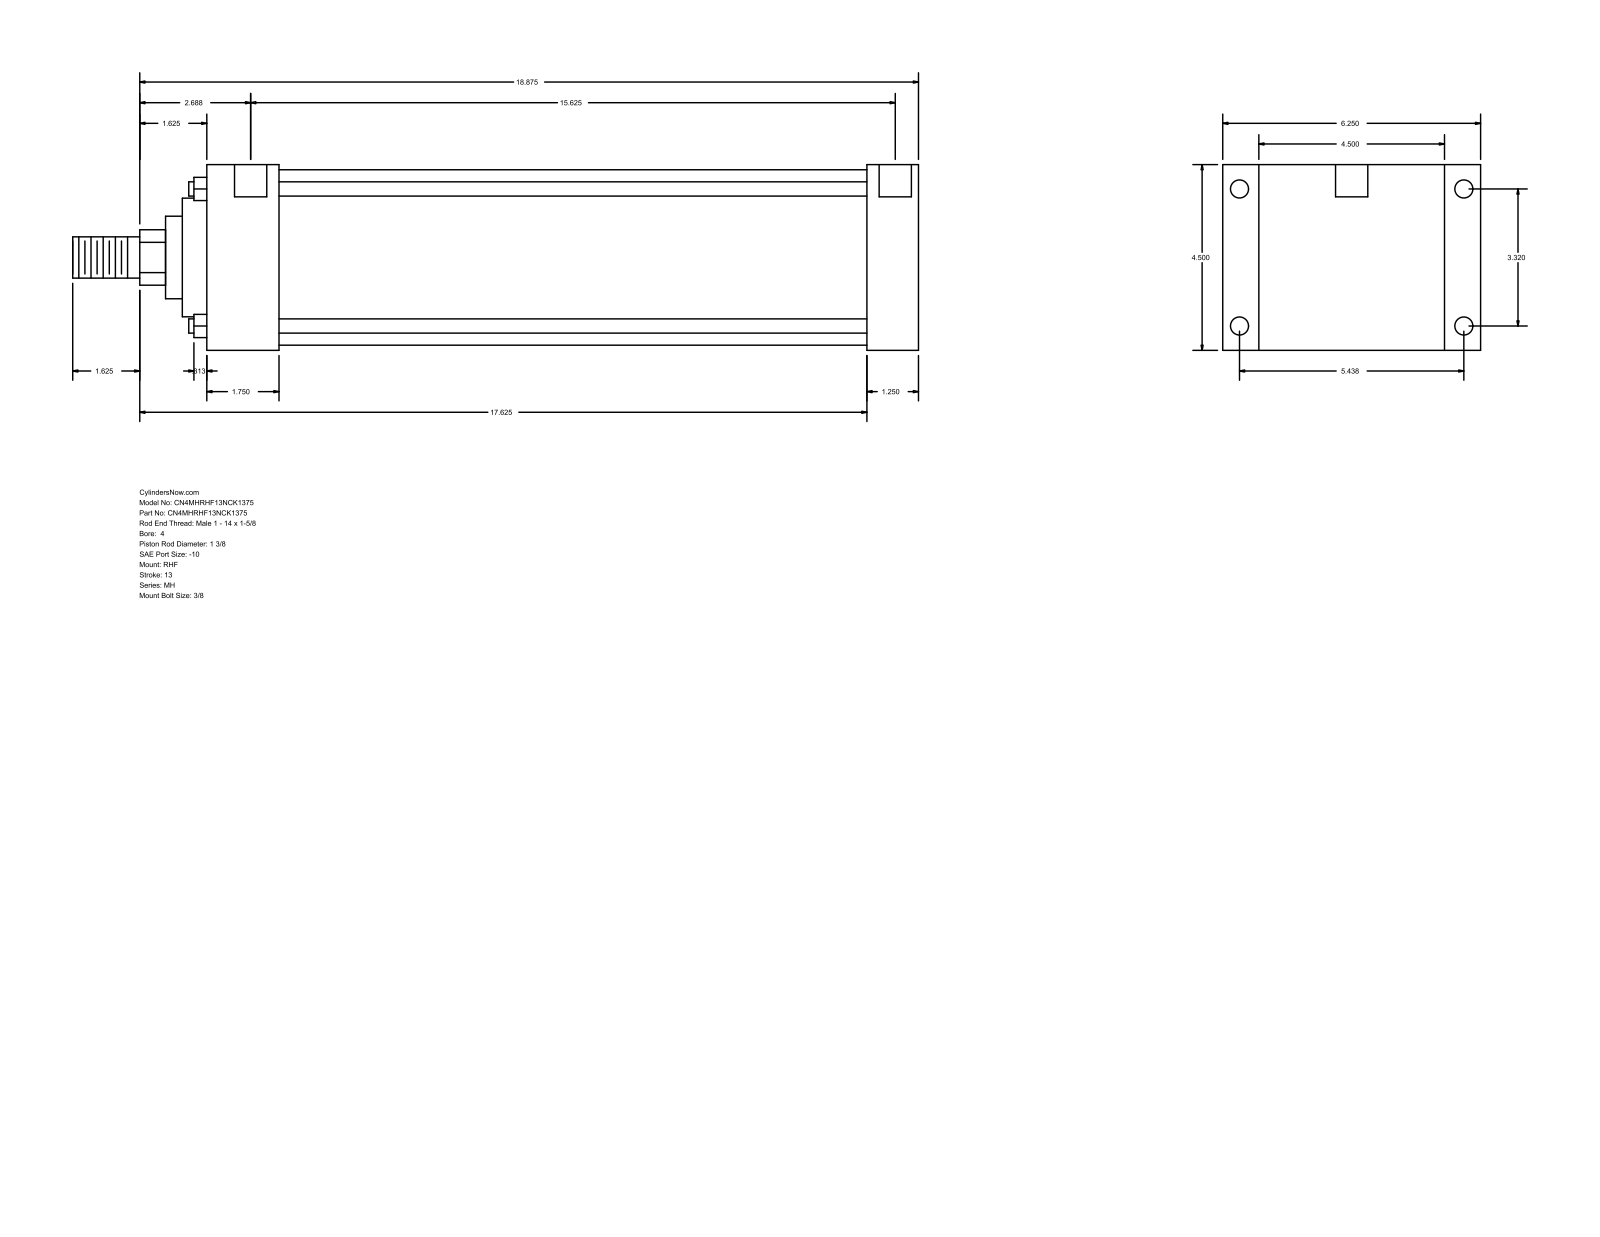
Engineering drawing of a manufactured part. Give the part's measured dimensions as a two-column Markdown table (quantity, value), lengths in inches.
| quantity | value |
| --- | --- |
| part name | MH_RHF__0400_1.375 |
| STEP written by | GSSL Pune (CONFIG_CONTROL_DESIGN) |
| units | inches |
| bodies | 0 solids, 90 faces (61 planar, 29 cylindrical, 0 other) |
| overall size | 20.5 × 6.25 × 4.5 |
| round holes (diameter × count) | 0.344 × 4, 0.438 × 4, 0.781 × 2 |
| round bosses / shafts (diameter × count) | 0.345 × 4, 4.25 × 1, 2.875 × 1, 2 × 1, 1.375 × 1, 1 × 1 |
| partial cylindrical surfaces (radius × count) | 0.672 × 1 |
| main face-to-face distances | 4.5, 1.25, 16, 17.25, 0.875, 5.375, 1.75, 14.25, 15.5, 6.25 |
| hole center spacings | 0.063, 3.32, 5.438, 6.371, 15.688, 15.75, 15.625 |
